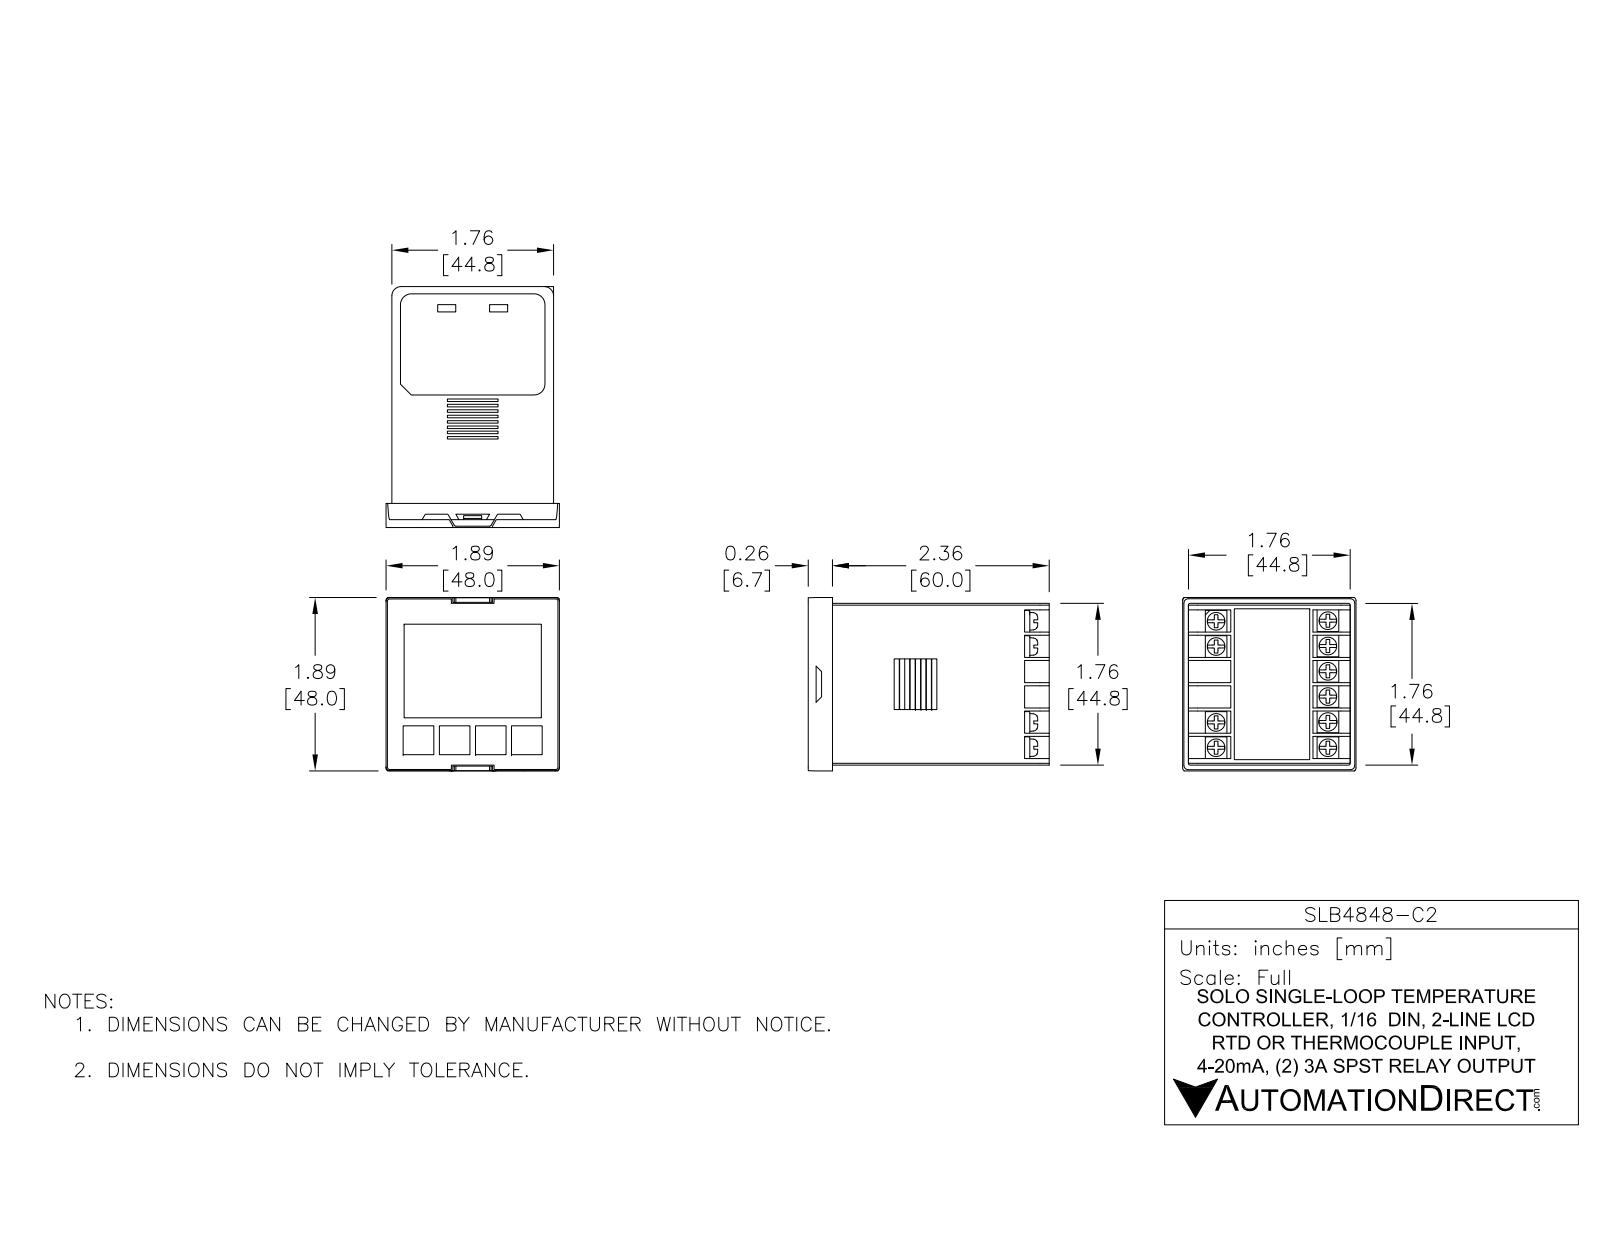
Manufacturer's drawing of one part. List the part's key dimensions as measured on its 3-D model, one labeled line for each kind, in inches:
Part name (STEP PRODUCT): SLB4848-C2
STEP written by: SolidWorks 2017 (AUTOMOTIVE_DESIGN)
Units: inches
Bodies: 8 solids, 3493 faces (3222 planar, 141 cylindrical, 130 other)
Overall size (bounding box): 2.628 × 2.234 × 1.89
Volume: 7.705 in³ · Surface area: 47.25 in²
Round bosses / shafts (diameter × count): ⌀0.21 ×2, ⌀0.114 ×2
Partial cylindrical surfaces — rounded edges, fillets, slot ends (radius × count): R0.006 ×36, R0.008 ×8, R0.02 ×6, R0.039 ×6, R0.024 ×4, R0.04 ×4, R0.063 ×4, R0.157 ×4
Main face-to-face distances: 1.762, 0.049, 1.813, 0.016, 1.746, 0.05, 1.763, 1.764, 1.763, 1.812
